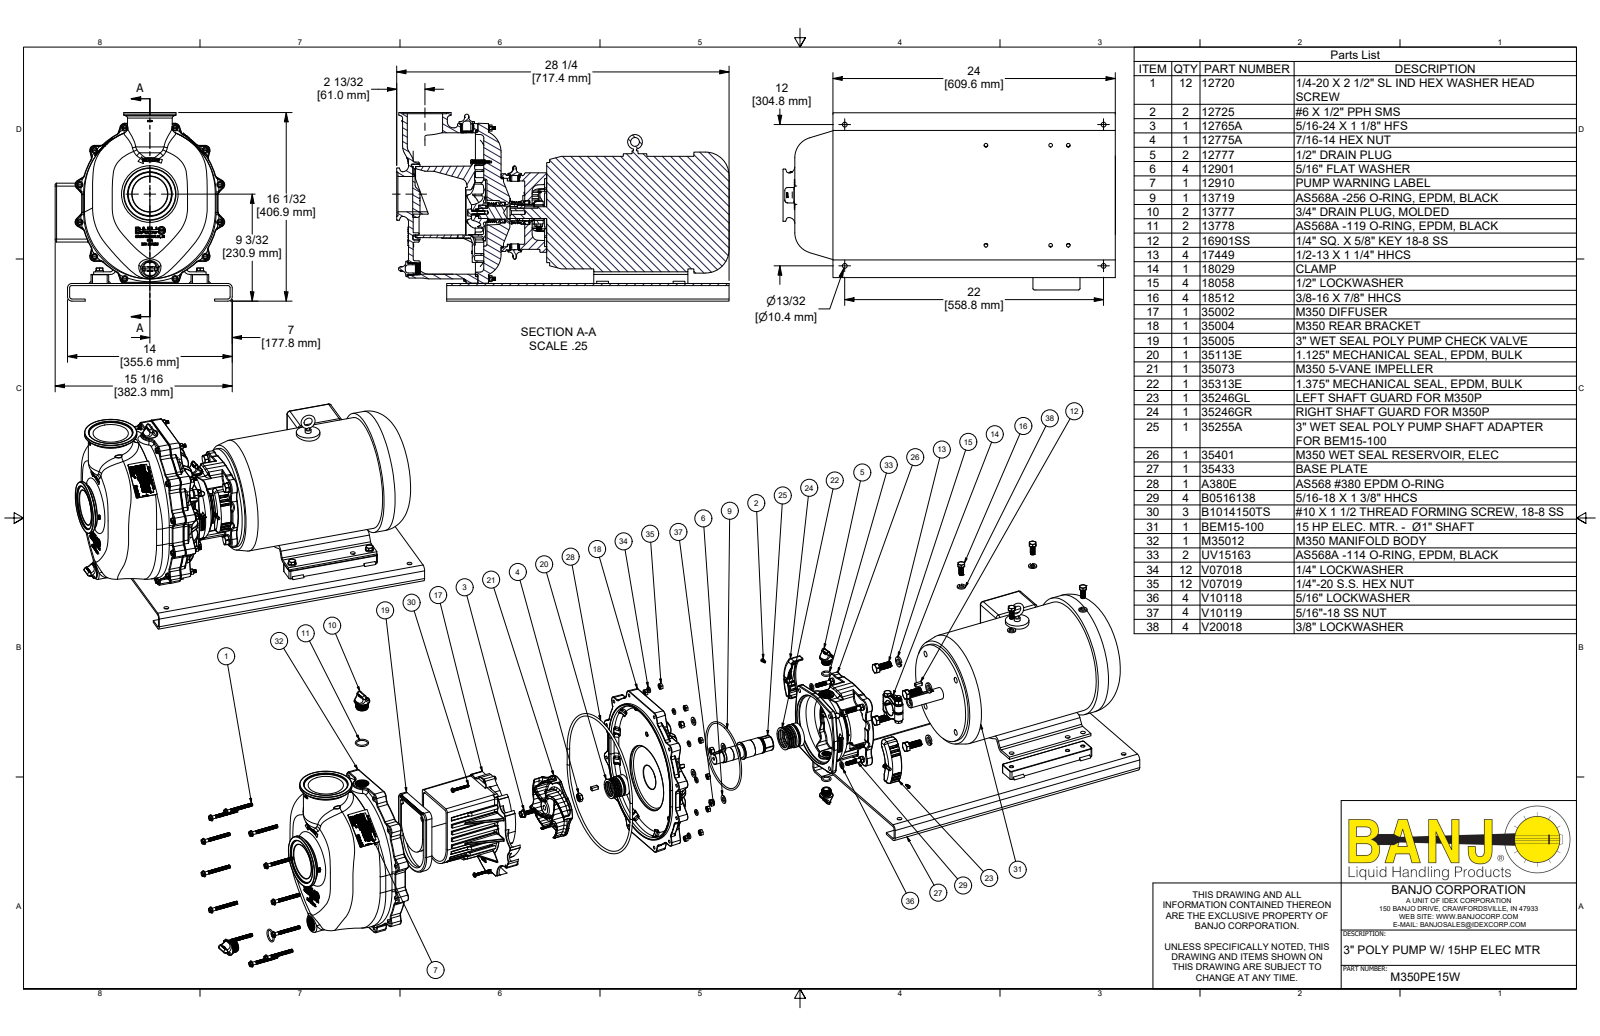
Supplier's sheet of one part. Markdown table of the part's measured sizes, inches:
| quantity | value |
| --- | --- |
| part name | M350PE15W; M35012; 35433; BEM15-100 (+8 more) |
| STEP written by | Autodesk Inventor 2022 (AUTOMOTIVE_DESIGN) |
| units | inches |
| bodies | 114 solids, 24861 faces (8740 planar, 3904 cylindrical, 12217 other) |
| overall size | 28.254 × 16.018 × 15.05 |
| volume | 1 646 in³ |
| surface area | 4 153 in² |
| round holes (diameter × count) | 0.196 × 12, 0.252 × 12, 0.27 × 12, 0.41 × 10, 0.52 × 10, 0.307 × 7, 0.385 × 6, 0.252 × 4, 0.313 × 4, 0.322 × 4, 0.344 × 4, 0.344 × 4 |
| round bosses / shafts (diameter × count) | 0.436 × 60, 0.324 × 52, 0.337 × 46, 0.25 × 13, 0.489 × 12, 0.5 × 7, 0.687 × 6, 0.375 × 6 |
| partial cylindrical surfaces (radius × count) | 0.031 × 357, 0.062 × 204, 0.016 × 75, 0.094 × 69, 0.125 × 60, 0.25 × 56, 0.375 × 50, 0.03 × 22 |
| main face-to-face distances | 0.179, 0.4, 1.5, 5.344, 1.321, 0.5, 4.944, 1.141, 1.32, 6.4 |
| hole center spacings | 6.005, 3.182, 5.117, 5.5, 7, 0.03, 8.53, 9.407 |
